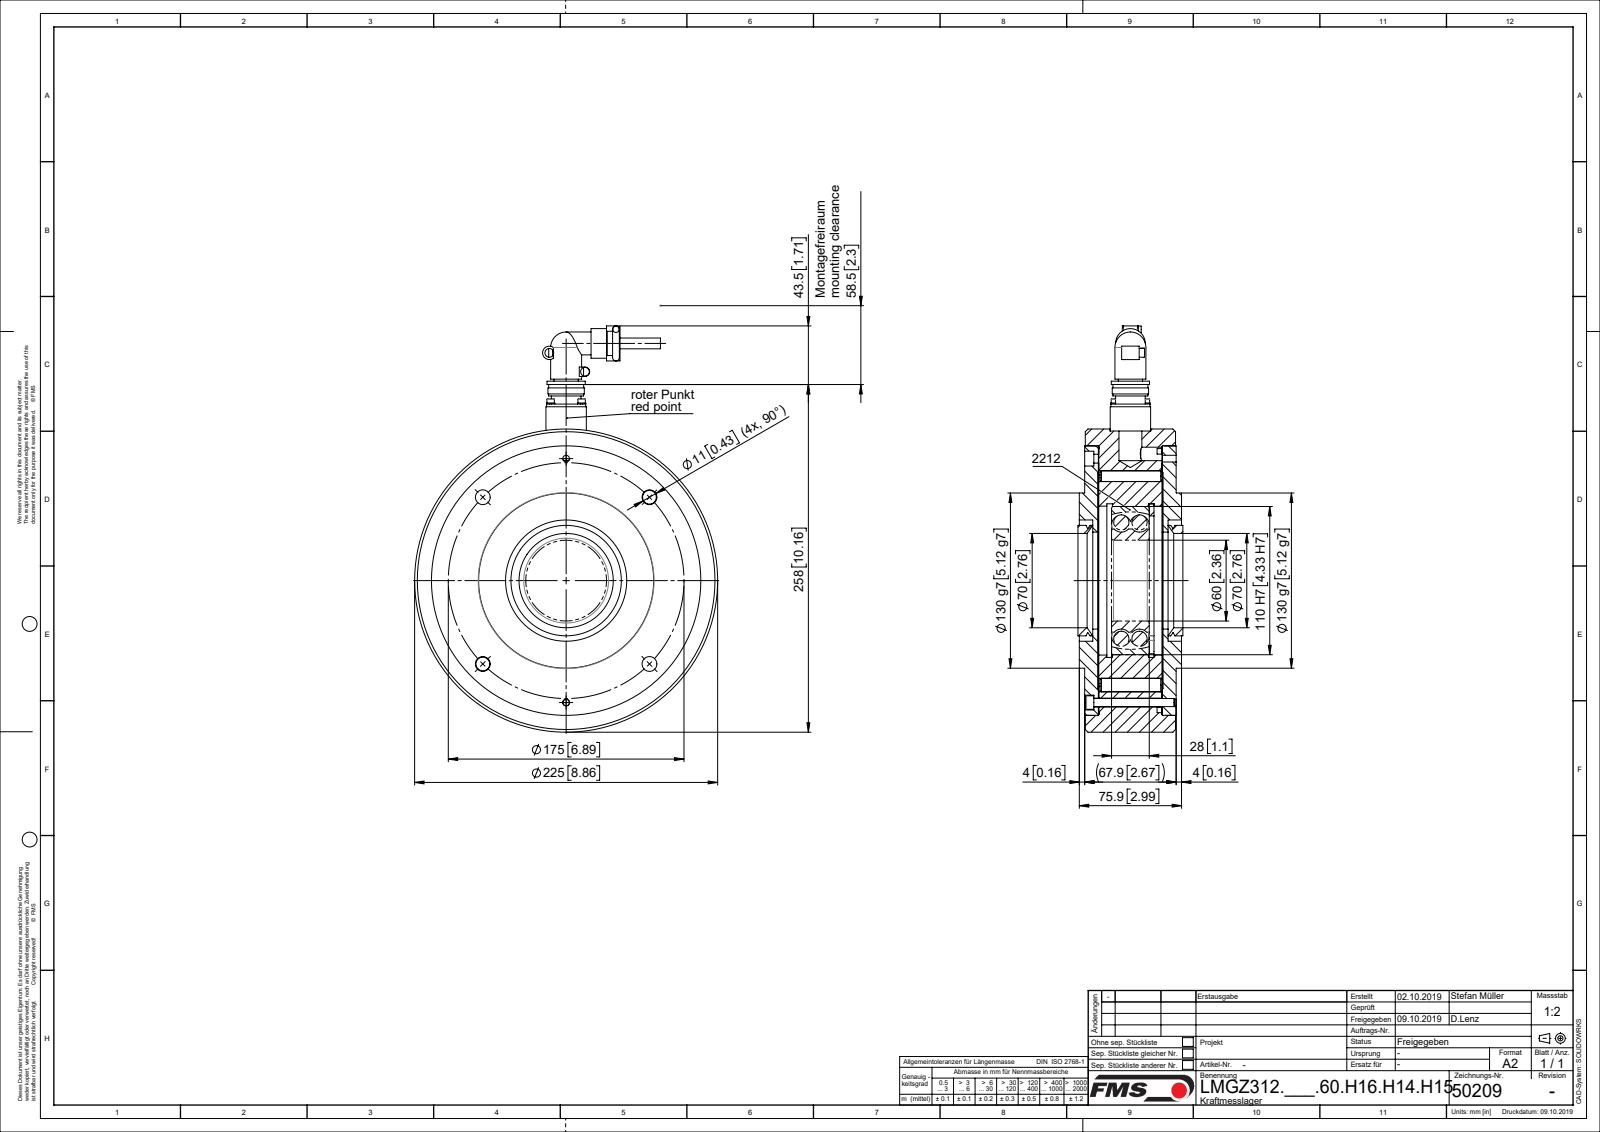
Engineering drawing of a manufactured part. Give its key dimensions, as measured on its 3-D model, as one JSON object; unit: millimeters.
{"part_name": "L50209; L4963304; TEIL1; L49258 (+8 more)", "step_written_by": "Mechanical Desktop 2007 (CONFIG_CONTROL_DESIGN)", "units": "millimeters", "bodies": {"solids": 20, "faces": 409, "planar": 120, "cylindrical": 232, "other": 57}, "overall_size": [301.5, 225, 77.9], "volume_mm3": 2386000, "surface_area_mm2": 393608, "round_holes": [[11, 6], [2.6, 4], [3.2, 4], [3.4, 4], [3.5, 4], [9, 4], [5, 2], [6.6, 2], [23, 1], [60, 1], [70, 1], [72, 1]], "round_bosses_or_shafts": [[6.2, 4], [5.5, 4], [3, 4], [22, 2], [6.5, 2], [4.8, 2], [225, 1], [199, 1]], "partial_cylinders_radius": [[2.5, 2], [3.5, 1], [5, 1], [81, 1], [86, 1]], "face_to_face_distances": [47.25, 10.45, 10.2, 57.45, 57.7, 47.5, 0.5, 48, 9.7, 58.2], "hole_center_spacings": [16.26, 23, 87.5, 32.53, 68.17, 68.18, 90.5, 123.74]}
